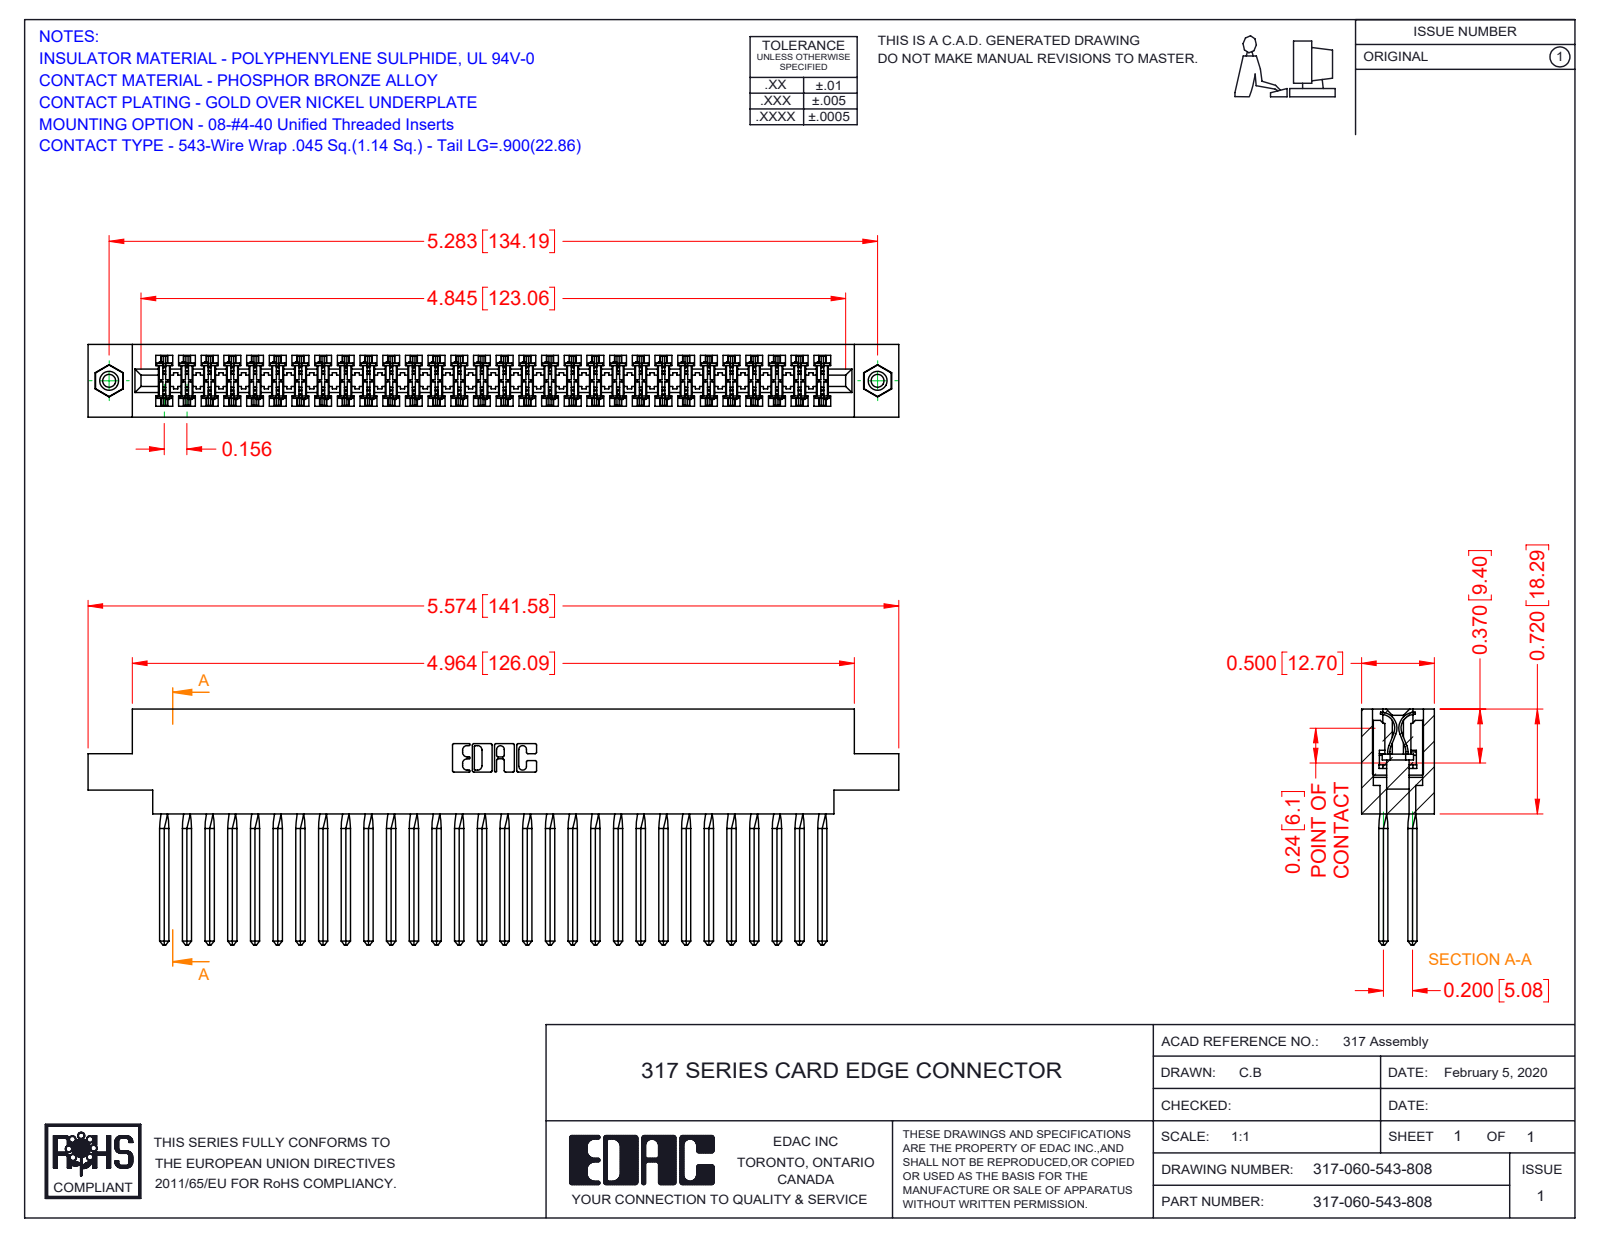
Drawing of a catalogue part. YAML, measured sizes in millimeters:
part_name: "317 Part_.156 Dia - TI; 317-060-543-878; 345-250-001_345-250-003-102; 317-290-001_543"
step_written_by: "SolidWorks 2016 (CONFIG_CONTROL_DESIGN)"
units: millimeters
bodies: {solids: 63, faces: 5502, planar: 4470, cylindrical: 776, other: 256}
overall_size: [141.6, 41.1, 12.7]
volume: 23650
surface_area: 35430
round_holes:
  - {diameter: 2.3, count: 2}
  - {diameter: 3.2, count: 2}
  - {diameter: 4, count: 2}
round_bosses_or_shafts:
  - {diameter: 3.9, count: 2}
partial_cylinders:
  - {radius: 0.4, count: 120}
  - {radius: 0.3, count: 22}
  - {radius: 0.2, count: 6}
  - {radius: 0.8, count: 6}
  - {radius: 0.7, count: 3}
  - {radius: 2.4, count: 2}
  - {radius: 2.5, count: 2}
  - {radius: 2.8, count: 2}
face_to_face_distances: [12.7, 1.9, 10.8, 8.9, 2.8, 5, 2.4, 5.1, 18.3, 2.9]
hole_center_spacings: [134.2]
